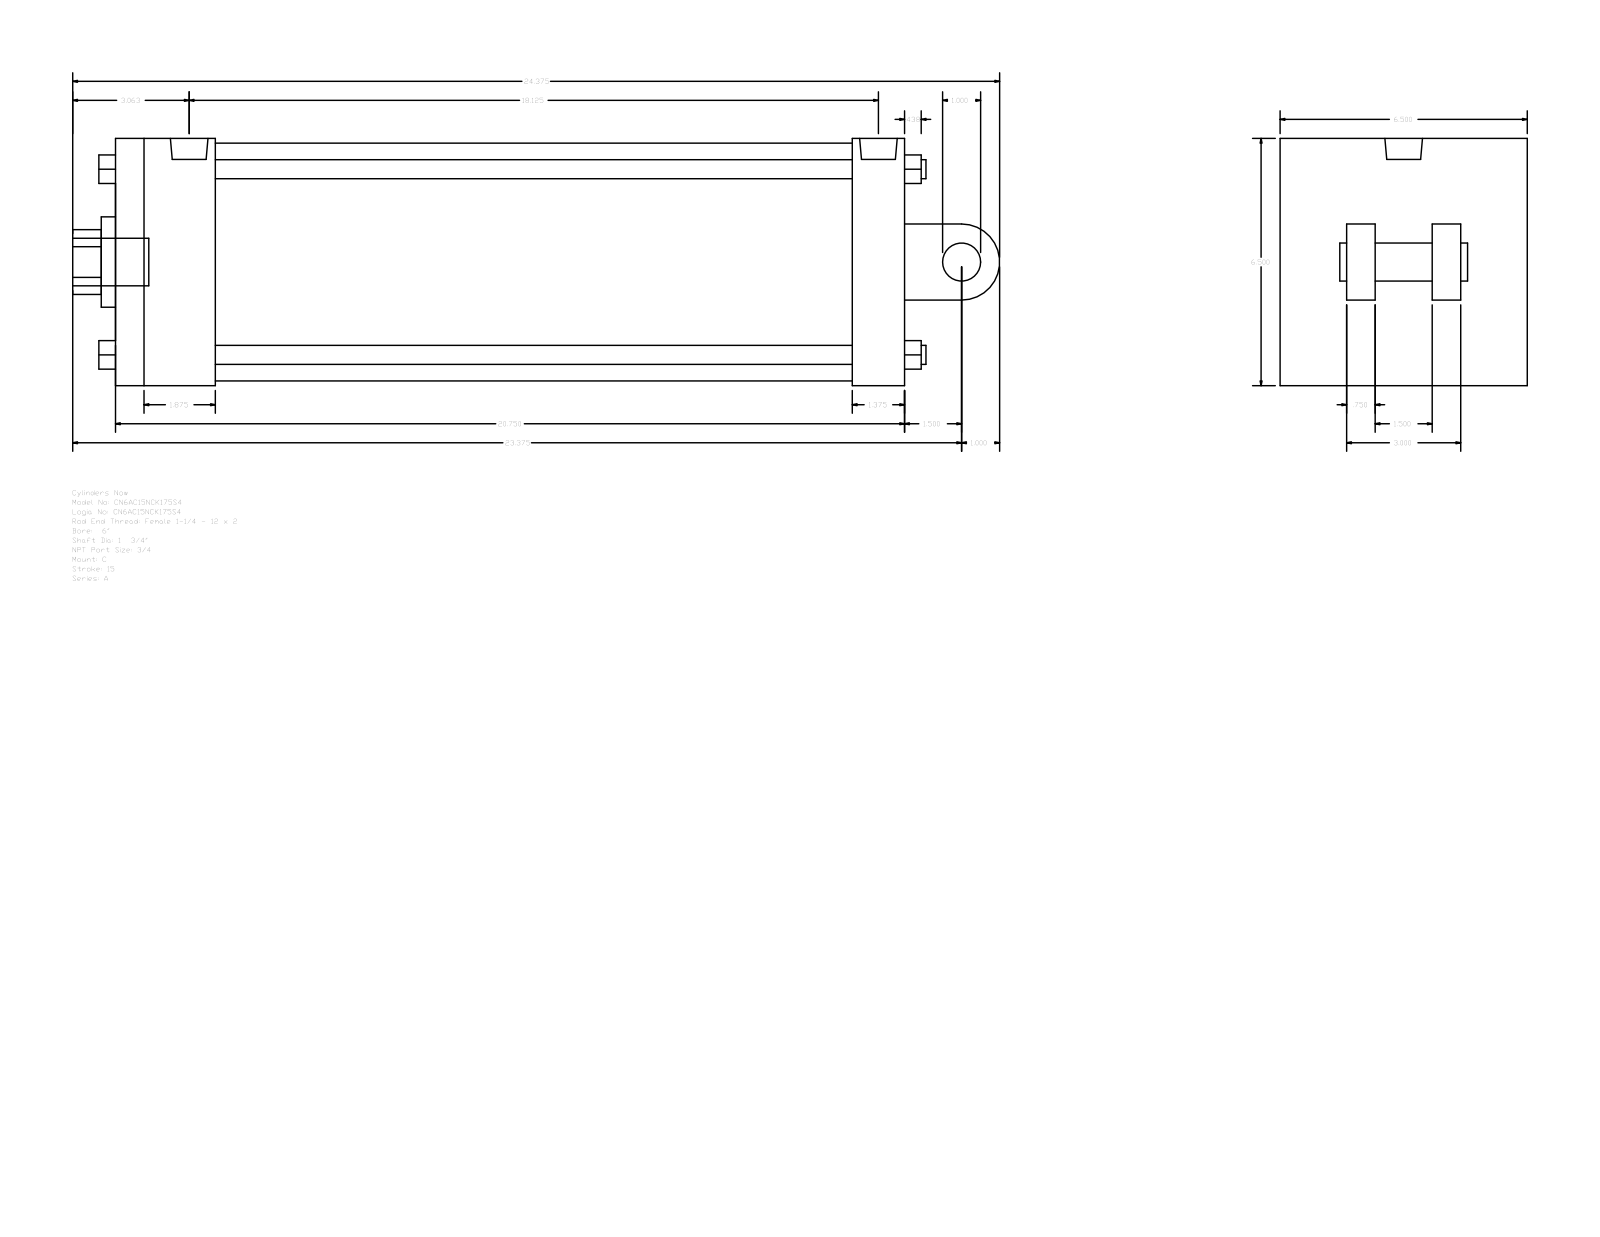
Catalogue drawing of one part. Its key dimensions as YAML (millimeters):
part_name: "A_C__0600_1.75"
step_written_by: "GSSL Pune (CONFIG_CONTROL_DESIGN)"
units: millimeters
bodies: {solids: 0, faces: 135, planar: 102, cylindrical: 33, other: 0}
overall_size: [619.12, 165.1, 165.1]
round_holes:
  - {diameter: 15.08, count: 2}
  - {diameter: 25.12, count: 1}
  - {diameter: 44.45, count: 1}
  - {diameter: 60.33, count: 1}
  - {diameter: 158.75, count: 1}
round_bosses_or_shafts:
  - {diameter: 12.7, count: 4}
  - {diameter: 15.08, count: 2}
  - {diameter: 31.75, count: 1}
  - {diameter: 25.4, count: 1}
  - {diameter: 25.12, count: 1}
partial_cylinders:
  - {radius: 21.63, count: 1}
  - {radius: 25.4, count: 1}
face_to_face_distances: [165.1, 527.05, 19.05, 57.15, 34.92, 66.68, 460.37, 492.13, 425.45, 44.45]
hole_center_spacings: [5.56]
